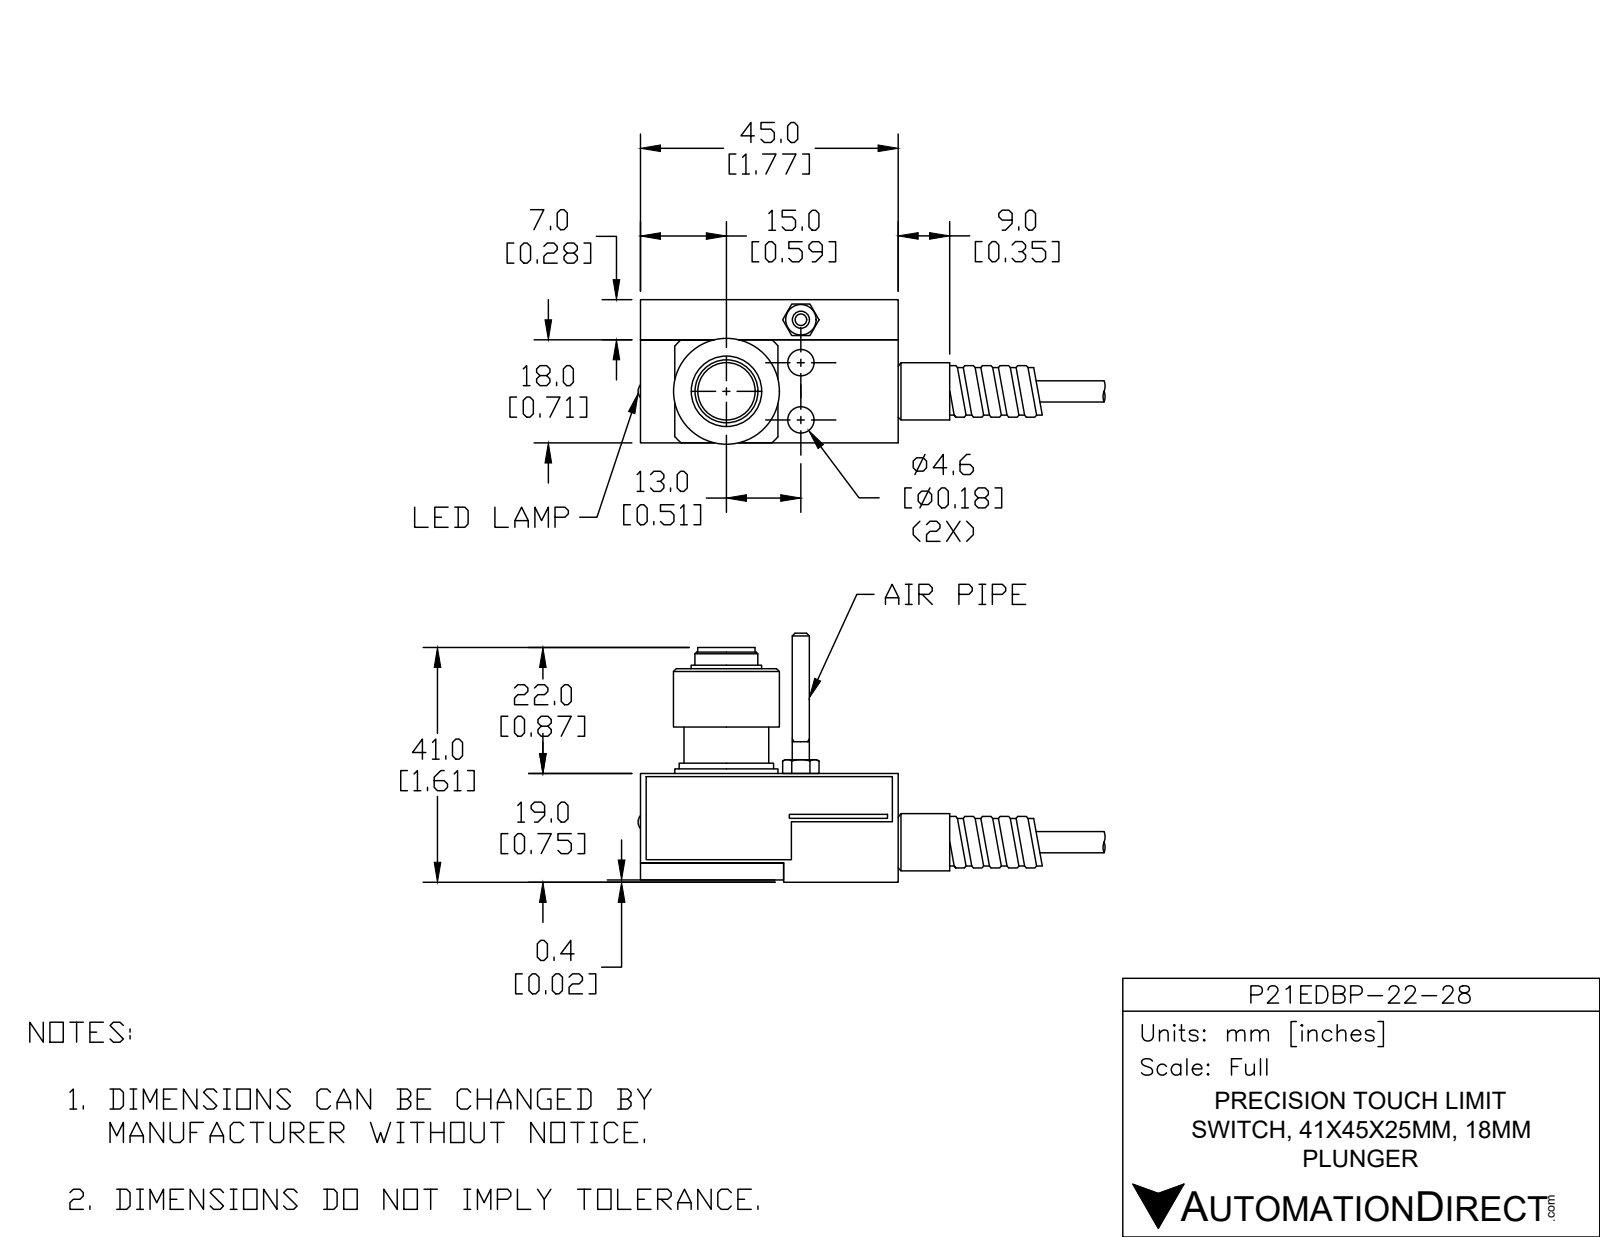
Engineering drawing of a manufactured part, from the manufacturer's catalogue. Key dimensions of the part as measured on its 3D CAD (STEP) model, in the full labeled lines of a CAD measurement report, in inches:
Part name (STEP PRODUCT): P21EDBP-22-28
STEP written by: SolidWorks 2017 (CONFIG_CONTROL_DESIGN)
Units: inches
Bodies: 1 solid, 367 faces (182 planar, 54 cylindrical, 131 other)
Overall size (bounding box): 3.167 × 1.713 × 0.994
Volume: 1.477 in³ · Surface area: 12.34 in²
Round holes (diameter × count): ⌀0.181 ×2, ⌀0.176 ×1
Round bosses / shafts (diameter × count): ⌀0.394 ×2, ⌀0.728 ×1, ⌀0.65 ×1, ⌀0.583 ×1, ⌀0.484 ×1, ⌀0.433 ×1, ⌀0.354 ×1, ⌀0.146 ×1
Partial cylindrical surfaces — rounded edges, fillets, slot ends (radius × count): R0.472 ×1
Main face-to-face distances: 0.732, 0.984, 0.276, 0.709, 0.985, 0.709, 1.772, 0.748, 0.354, 0.016
Hole centre spacings: 0.394
